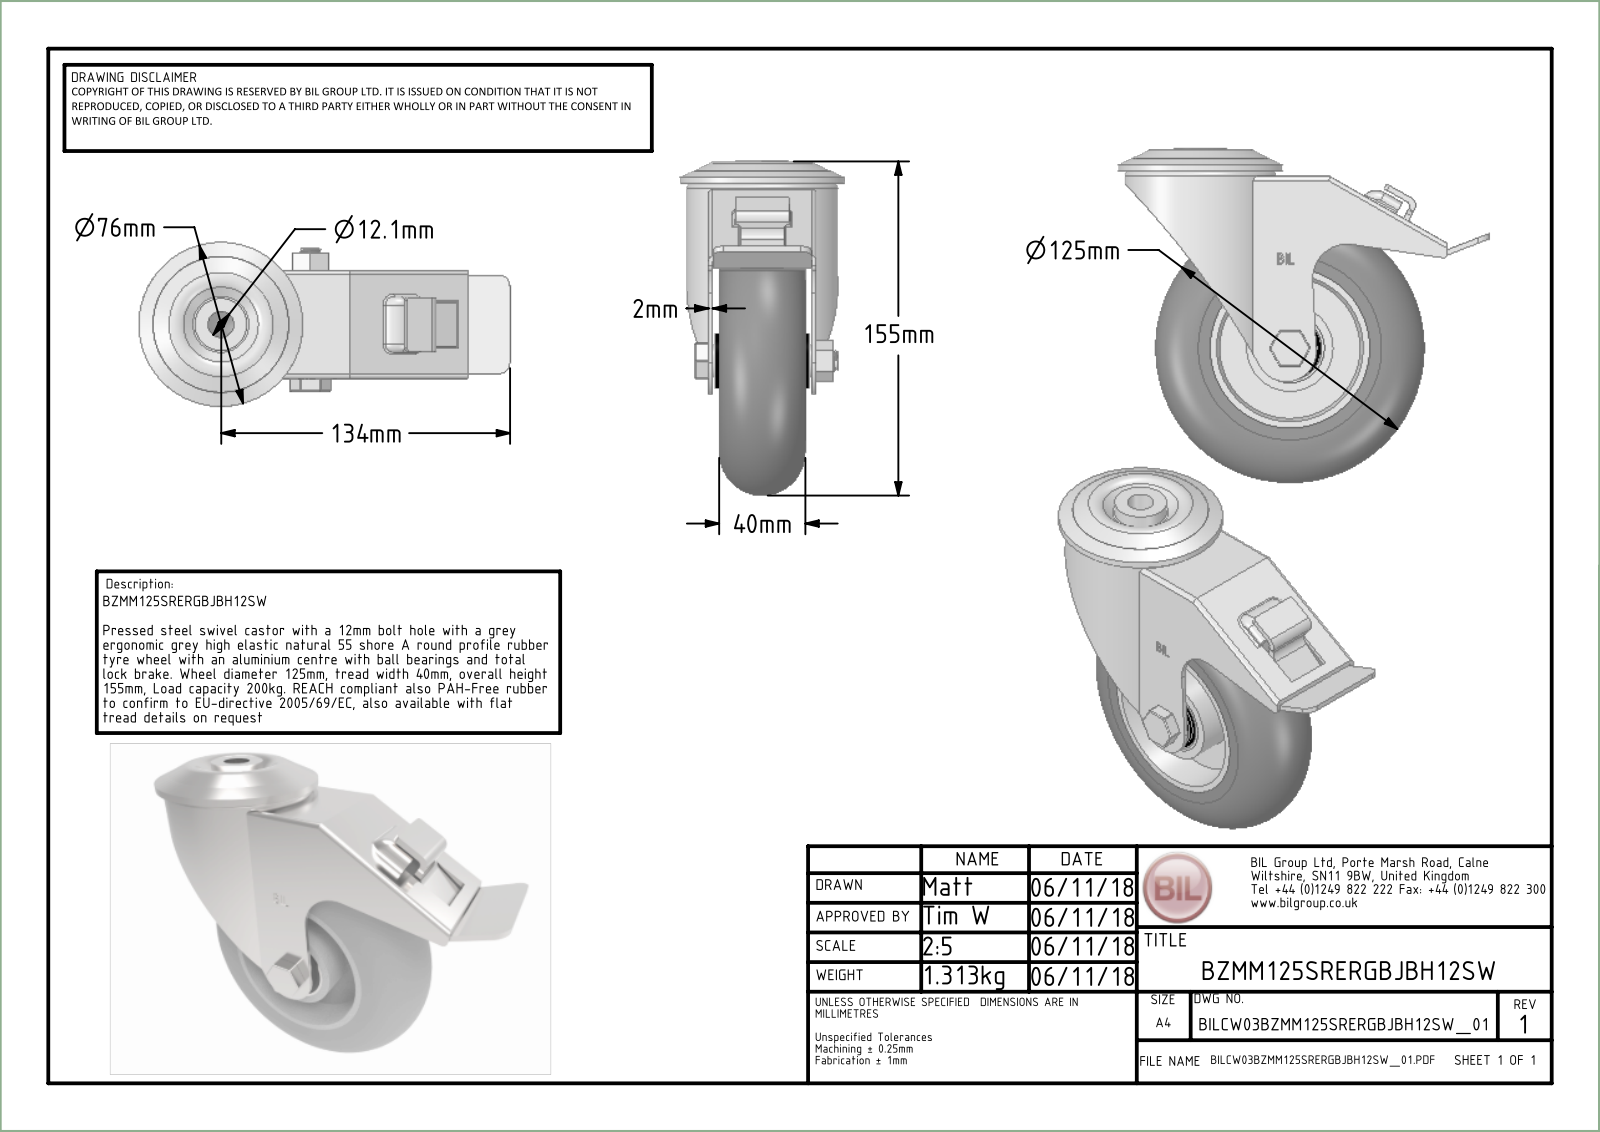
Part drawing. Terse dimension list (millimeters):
name: BZMM125SRERGBJBH12SW v3; BZMM125ASBH12SWB v2; ZINC PLATED, PRESSED STEEL HEAD; ZINC PLATED, PRESSED STEEL FORKS (+8 more)
written by: Autodesk Translation Framework v13.20.0.188 (AP242_MANAGED_MODEL_BASED_3D_ENGINEERING_MIM_LF)
unit: mm
bodies: 43 solids, 1388 faces (552 planar, 297 cylindrical, 539 other)
size: 172 × 155 × 76
volume: 443 415 mm³; area: 164 459 mm²
holes: 2× ⌀6, 1× ⌀9, 1× ⌀10, 1× ⌀10.2, 1× ⌀12, 1× ⌀12.2, 1× ⌀15, 1× ⌀15.75, 1× ⌀20.5, 1× ⌀26, 1× ⌀26.8, 1× ⌀28
bosses: 1× ⌀70, 1× ⌀49.5, 1× ⌀40, 1× ⌀38, 1× ⌀25, 1× ⌀24, 1× ⌀21.5, 1× ⌀21.31
rounds: 60× R0.75, 32× R0.5, 7× R1.5, 6× R1.25, 6× R3, 6× R4, 5× R2.5, 3× R2
face distances: 2.5, 45, 47.5, 5, 42.5, 15.75, 29.25, 20.75, 18.25, 26.75
hole spacings: 52.5
